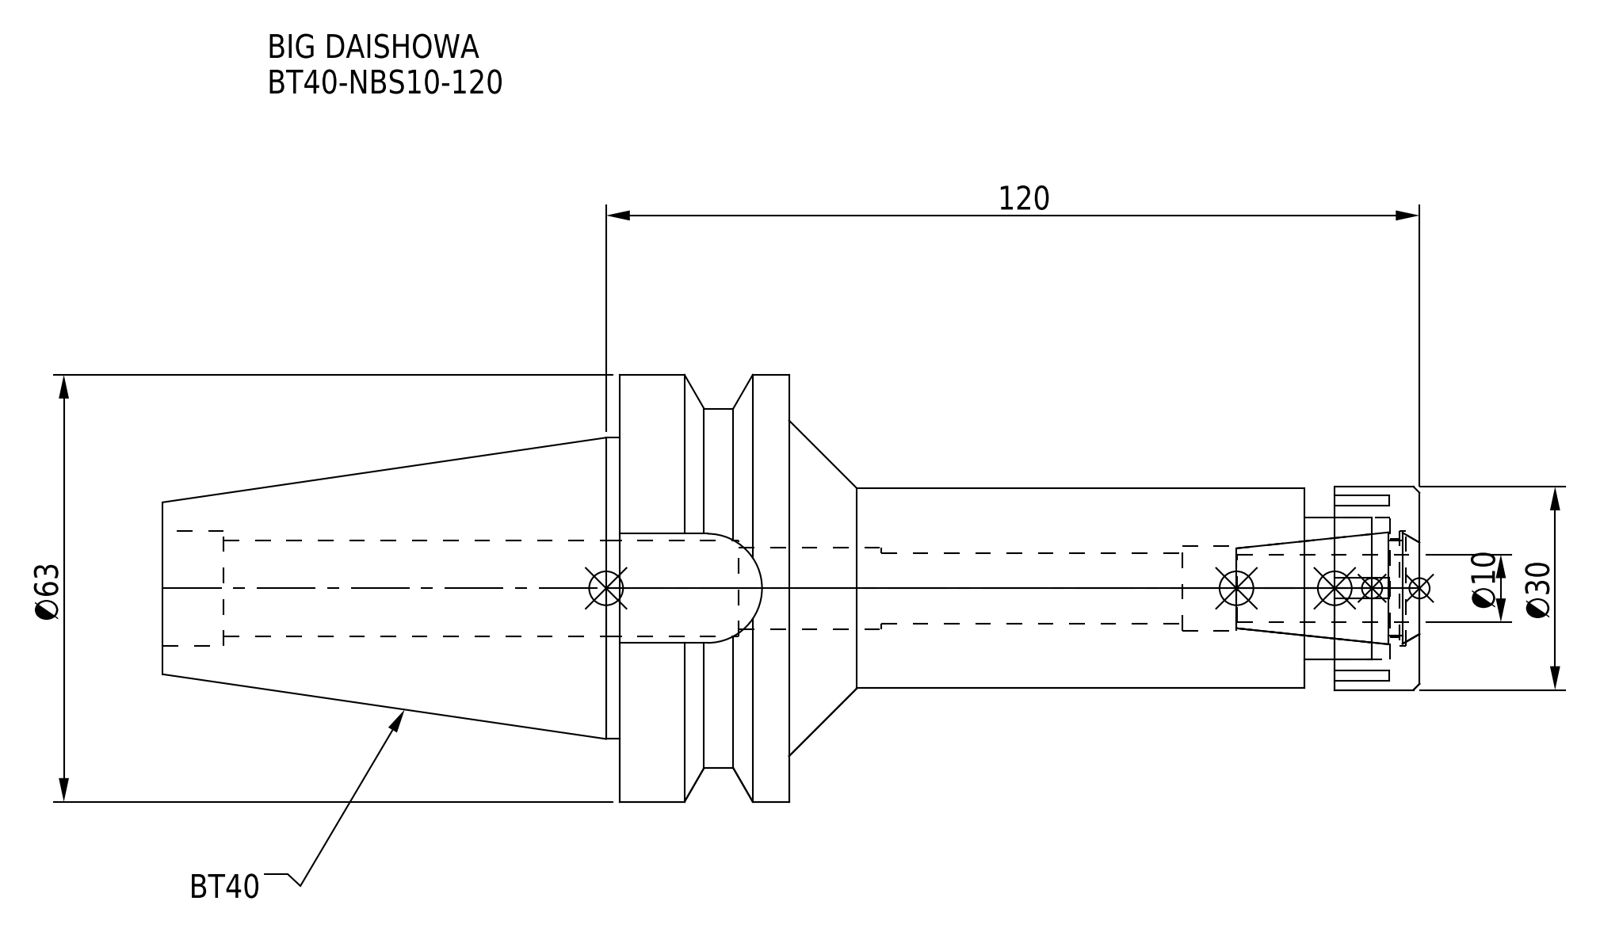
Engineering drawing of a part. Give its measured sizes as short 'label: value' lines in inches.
name: BT40-NBS10-120.stp; BT40-NBS10-120; BT40NB10120-100_ASM.stp; DXF_TEMP_ASSY_ASM_4_ASM.stp (+3 more)
written by: SolidWorks 2019 (CONFIG_CONTROL_DESIGN)
unit: in
bodies: 2 solids, 93 faces (45 planar, 34 cylindrical, 14 other)
size: 7.299 × 2.48 × 2.48
volume: 10.74 in³; area: 56.35 in²
holes: 1× ⌀0.409, 1× ⌀0.472, 1× ⌀0.492, 1× ⌀0.559, 1× ⌀0.571, 1× ⌀0.669, 1× ⌀0.827
bosses: 1× ⌀2.48, 1× ⌀2.087, 1× ⌀1.75, 1× ⌀1.181, 1× ⌀1.161
rounds: 1× R0.317
face distances: 0.984, 3.661, 4.646, 2.992, 0.177, 0.492, 0.669, 3.976, 3.169, 4.154
